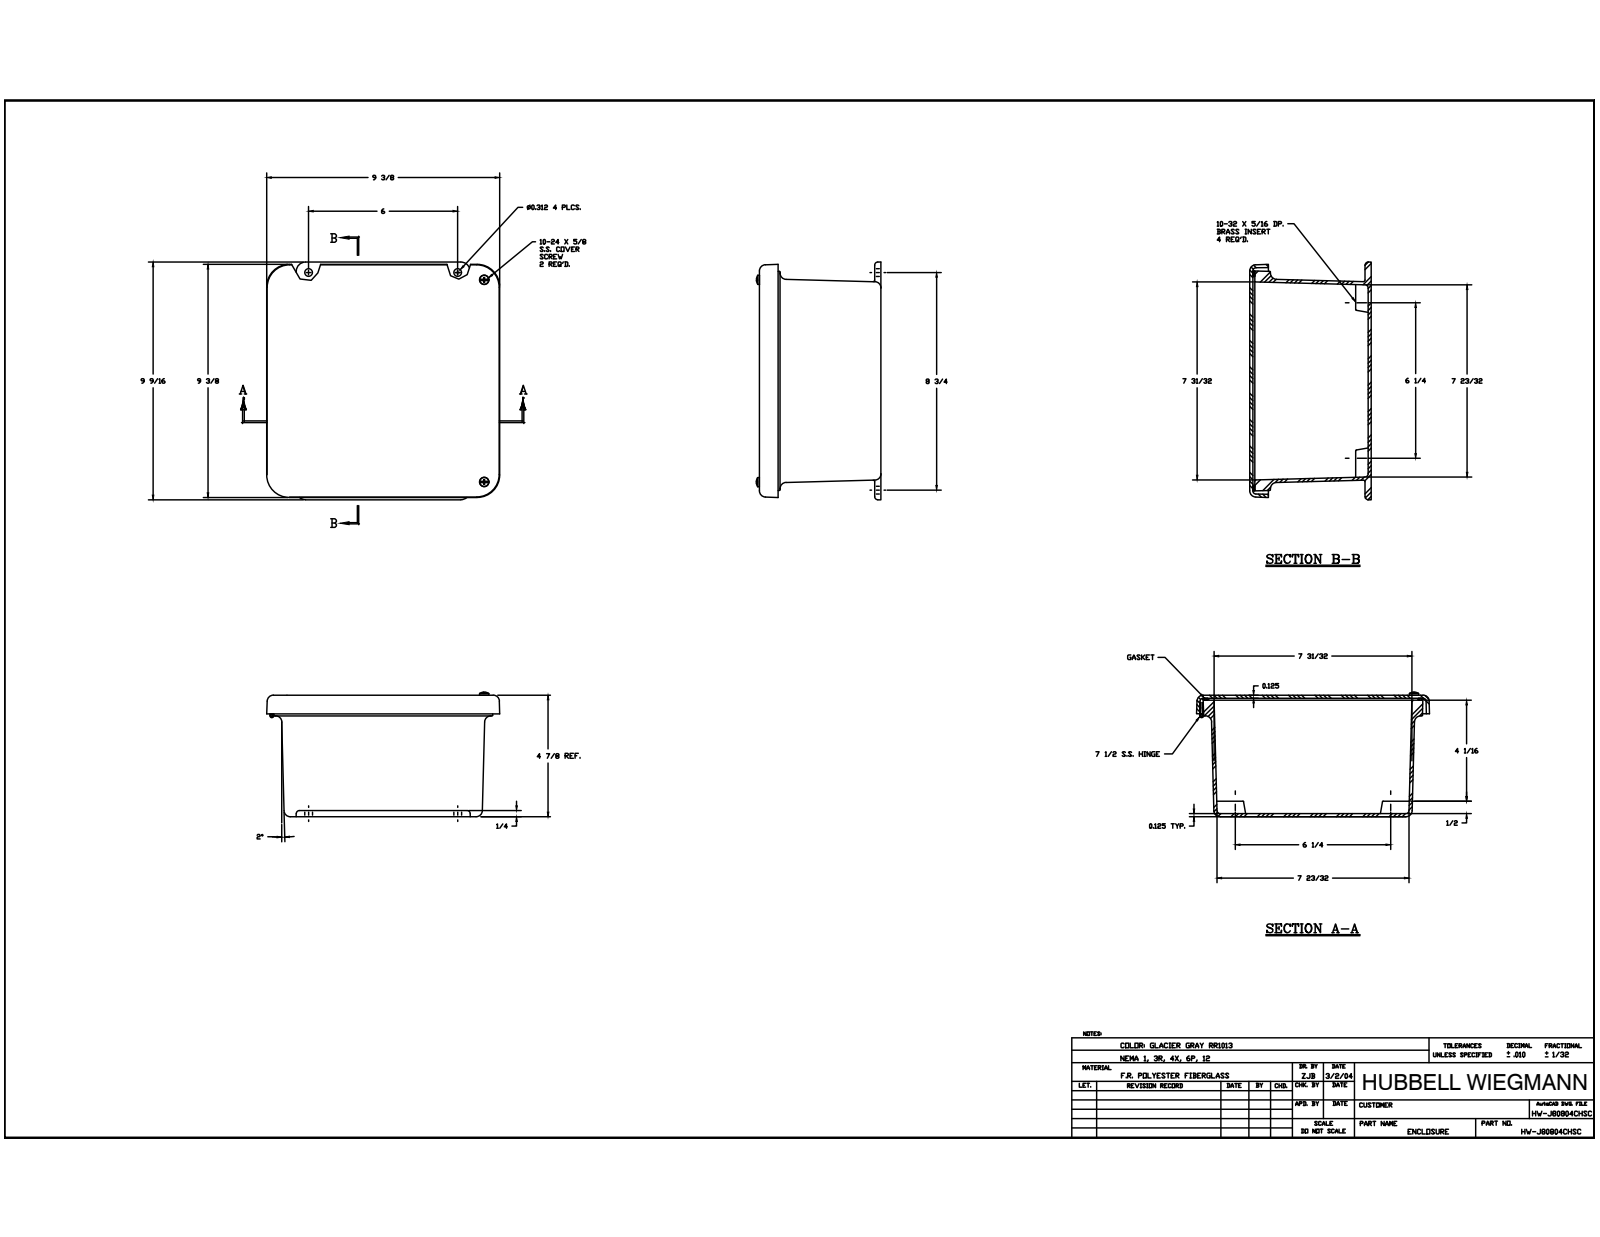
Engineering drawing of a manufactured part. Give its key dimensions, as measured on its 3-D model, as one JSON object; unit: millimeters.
{"part_name": "J808HW_1; RMINS45821P_21; RMINS45821P_22; RMINS45821P_23 (+8 more)", "step_written_by": "Autodesk Inventor 2014 (AUTOMOTIVE_DESIGN)", "units": "millimeters", "bodies": {"solids": 20, "faces": 797, "planar": 244, "cylindrical": 302, "other": 251}, "overall_size": [242.86, 238.94, 127.47], "volume_mm3": 843638, "surface_area_mm2": 475227, "round_holes": [[3.86, 8], [3.33, 6], [3.56, 6], [3.96, 4], [5.54, 4], [3.68, 2], [2.16, 1]], "round_bosses_or_shafts": [[6.86, 6], [6.35, 6], [3.17, 6], [4.83, 2], [3.97, 2], [3.94, 1]], "partial_cylinders_radius": [[0.79, 36], [3.17, 12], [6.35, 12], [5.08, 6], [0.79, 4], [9.53, 4], [1.6, 2]], "face_to_face_distances": [3.17, 120.97, 124.14, 117.79, 3.18, 120.96, 115.82, 5.14, 1.97, 119], "hole_center_spacings": [184.12, 88.9, 33.67, 158.76, 206.38, 258.19, 6.35, 82.55]}
